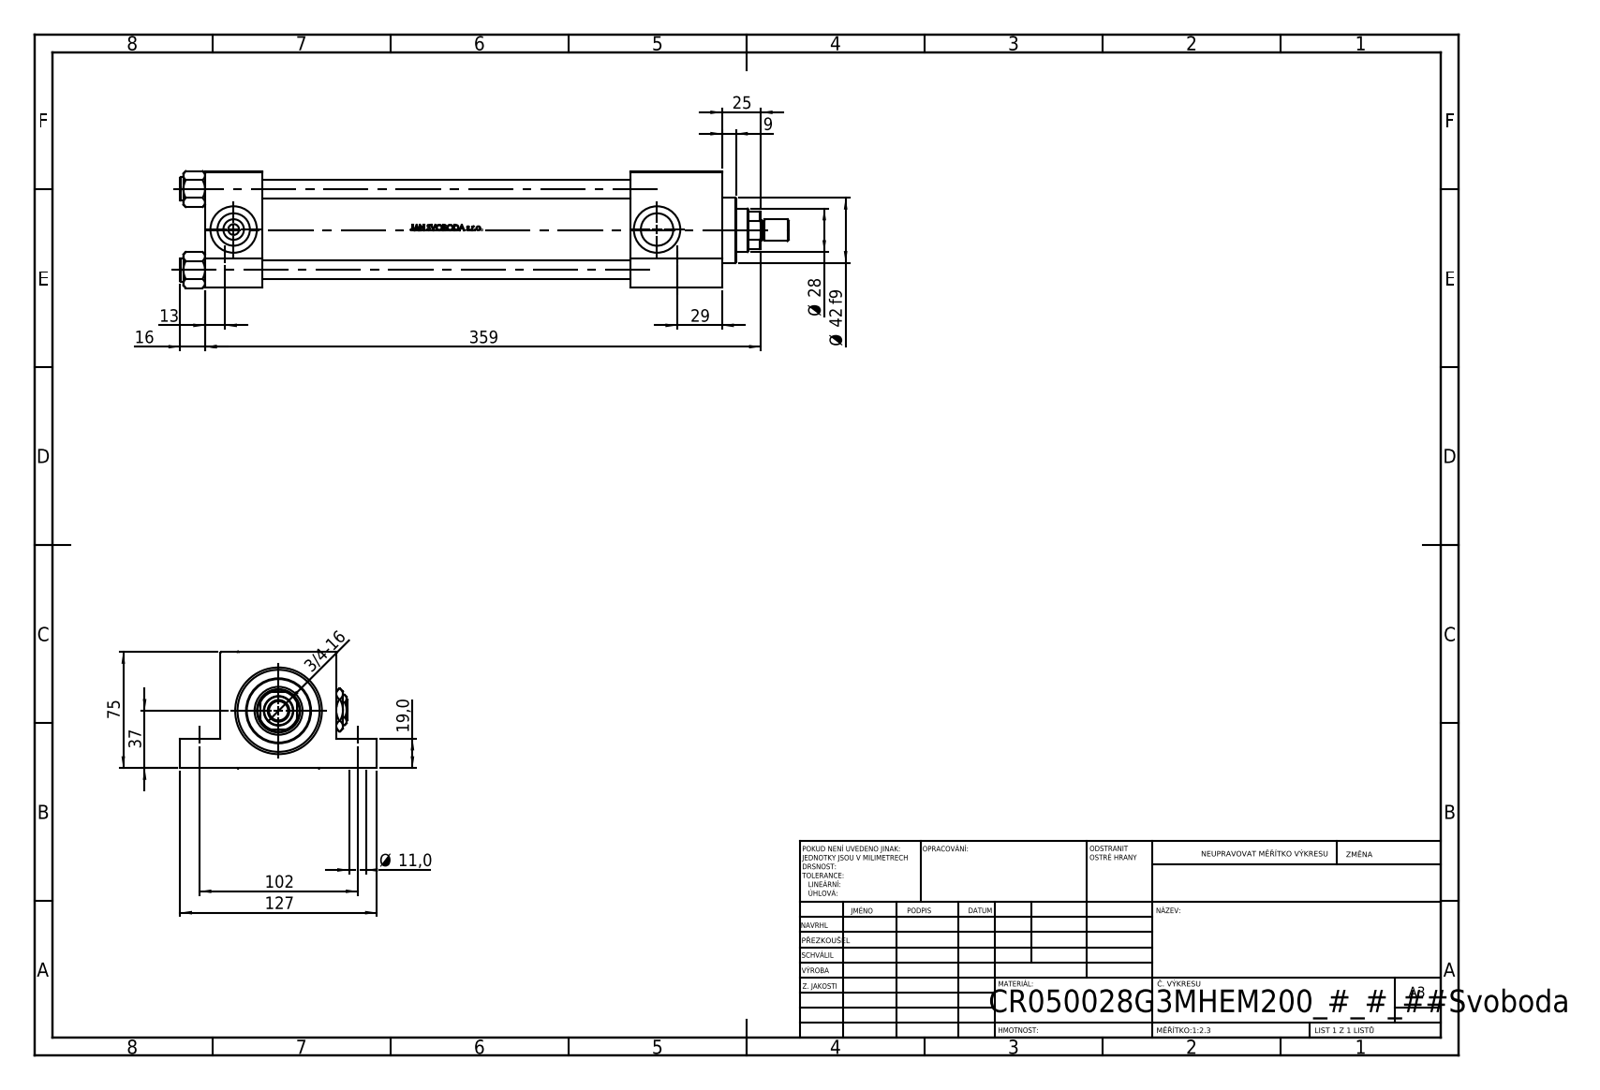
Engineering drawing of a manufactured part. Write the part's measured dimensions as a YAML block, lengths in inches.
part_name: "NUT_M5_G; Zatka_pro_OIL_PORT; V215_VC_A; V215CR_G_TYCINKA (+3 more)"
step_written_by: "SolidWorks 2019 (CONFIG_CONTROL_DESIGN)"
units: inches
bodies: {solids: 14, faces: 1197, planar: 481, cylindrical: 136, other: 580}
overall_size: [15.472, 5, 2.974]
volume: 63.89
surface_area: 421
round_holes:
  - {diameter: 0.433, count: 4}
  - {diameter: 0.472, count: 4}
  - {diameter: 0.276, count: 2}
  - {diameter: 0.825, count: 2}
  - {diameter: 1.181, count: 2}
  - {diameter: 0.728, count: 1}
  - {diameter: 1.102, count: 1}
  - {diameter: 1.22, count: 1}
  - {diameter: 1.614, count: 1}
  - {diameter: 1.969, count: 1}
  - {diameter: 2.087, count: 1}
round_bosses_or_shafts:
  - {diameter: 0.591, count: 4}
  - {diameter: 2.205, count: 1}
  - {diameter: 1.654, count: 1}
  - {diameter: 0.551, count: 1}
  - {diameter: 0.472, count: 1}
partial_cylinders:
  - {radius: 0.531, count: 1}
face_to_face_distances: [2.953, 1.457, 13.15, 11.693, 0.748, 2.205, 10.827, 9.37, 2.323, 1.024]
hole_center_spacings: [2.059, 1.442, 1.47, 2.912, 4.016, 11.496, 12.177, 10.768]
